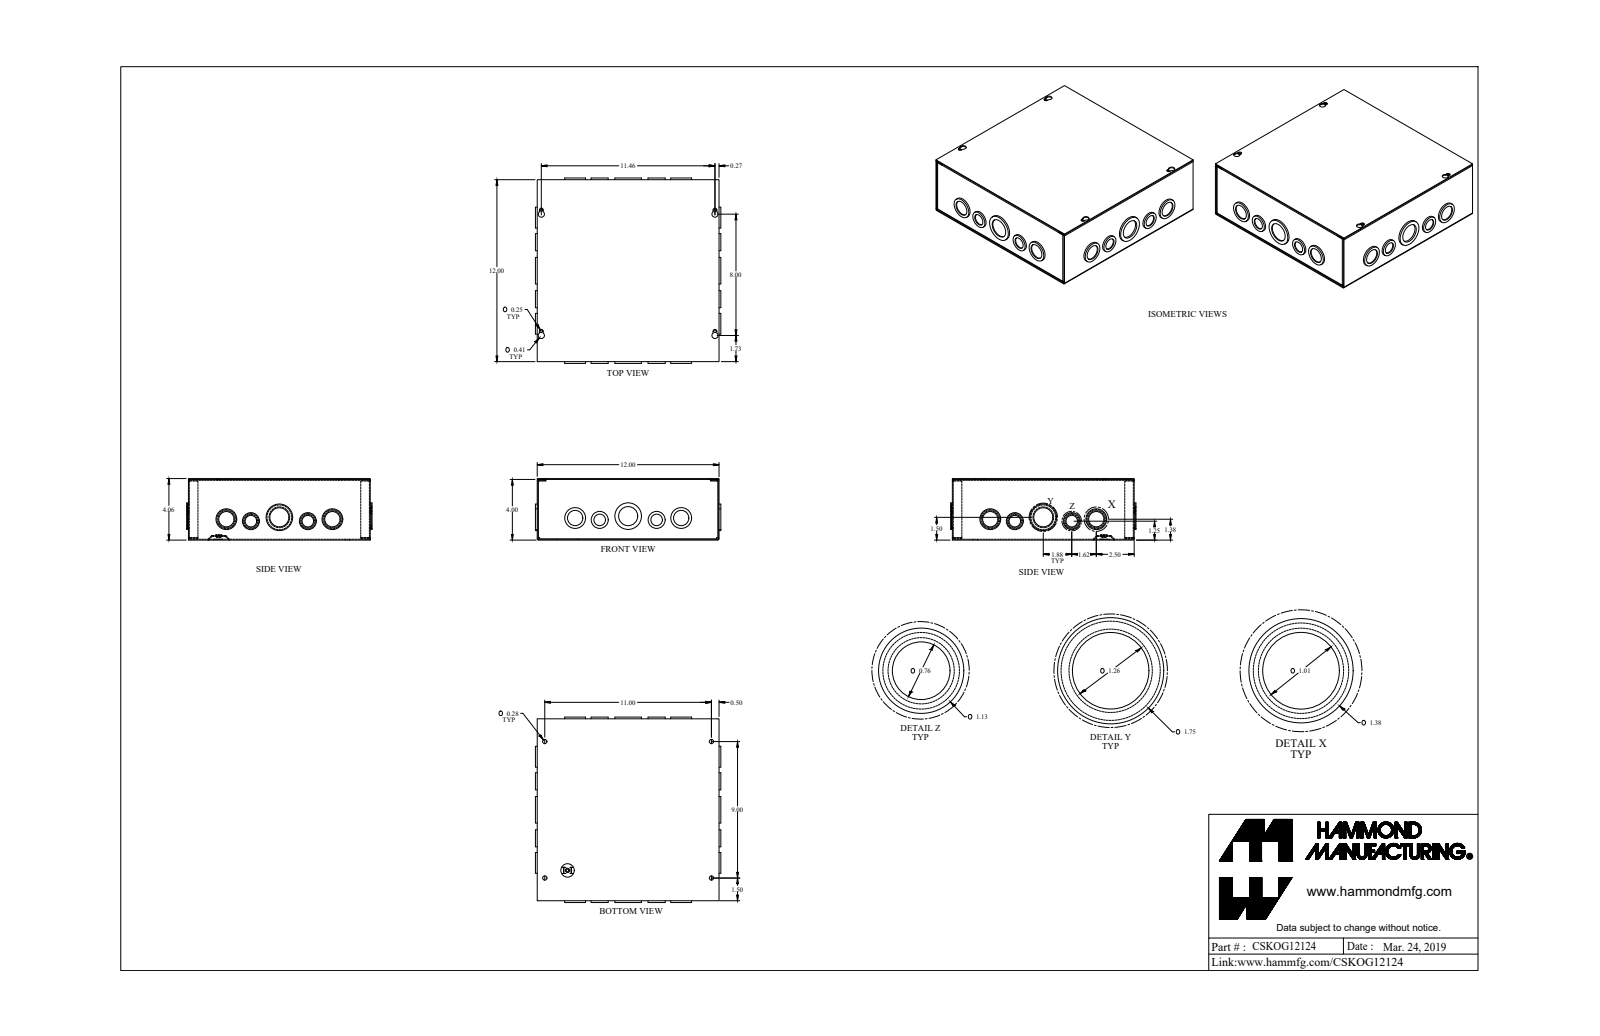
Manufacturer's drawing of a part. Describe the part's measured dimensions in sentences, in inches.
The part is named "CSKOG12124_Default". Its 3-D file was written by "SolidWorks 2019 (CONFIG_CONTROL_DESIGN)". It is 4 solids with 445 faces: 205 planar, 232 cylindrical and 8 other. Overall it measures 12.234 by 12.234 by 4.057 inches. Its volume is 30.09 cubic inches and its surface area 1 067 square inches. Round holes: 8 of diameter 1.011, 6 of diameter 1.261, 5 of diameter 0.17, 4 of diameter 0.281, 4 of diameter 0.761, 2 of diameter 1.636, 1 of diameter 0.5. Round bosses or shafts: 6 of diameter 1.125, 5 of diameter 1.375, 4 of diameter 0.875, 2 of diameter 1.75, 2 of diameter 1.125, 2 of diameter 0.875, 1 of diameter 1.375, 1 of diameter 0.492. Partial cylindrical surfaces (rounded edges, fillets, slot ends): 12 of radius 0.029, 12 of radius 0.086, 8 of radius 0.057, 4 of radius 0.125, 4 of radius 0.203. The main face-to-face distances are 0.057, 4, 3.943, 11.943, 4.057, 12, 11.886, 0.114, 0.08, 3.863. The hole center spacings are 0.55, 1.625, 1.896, 3.502, 5.381, 8.503, 11.241, 14.084.
